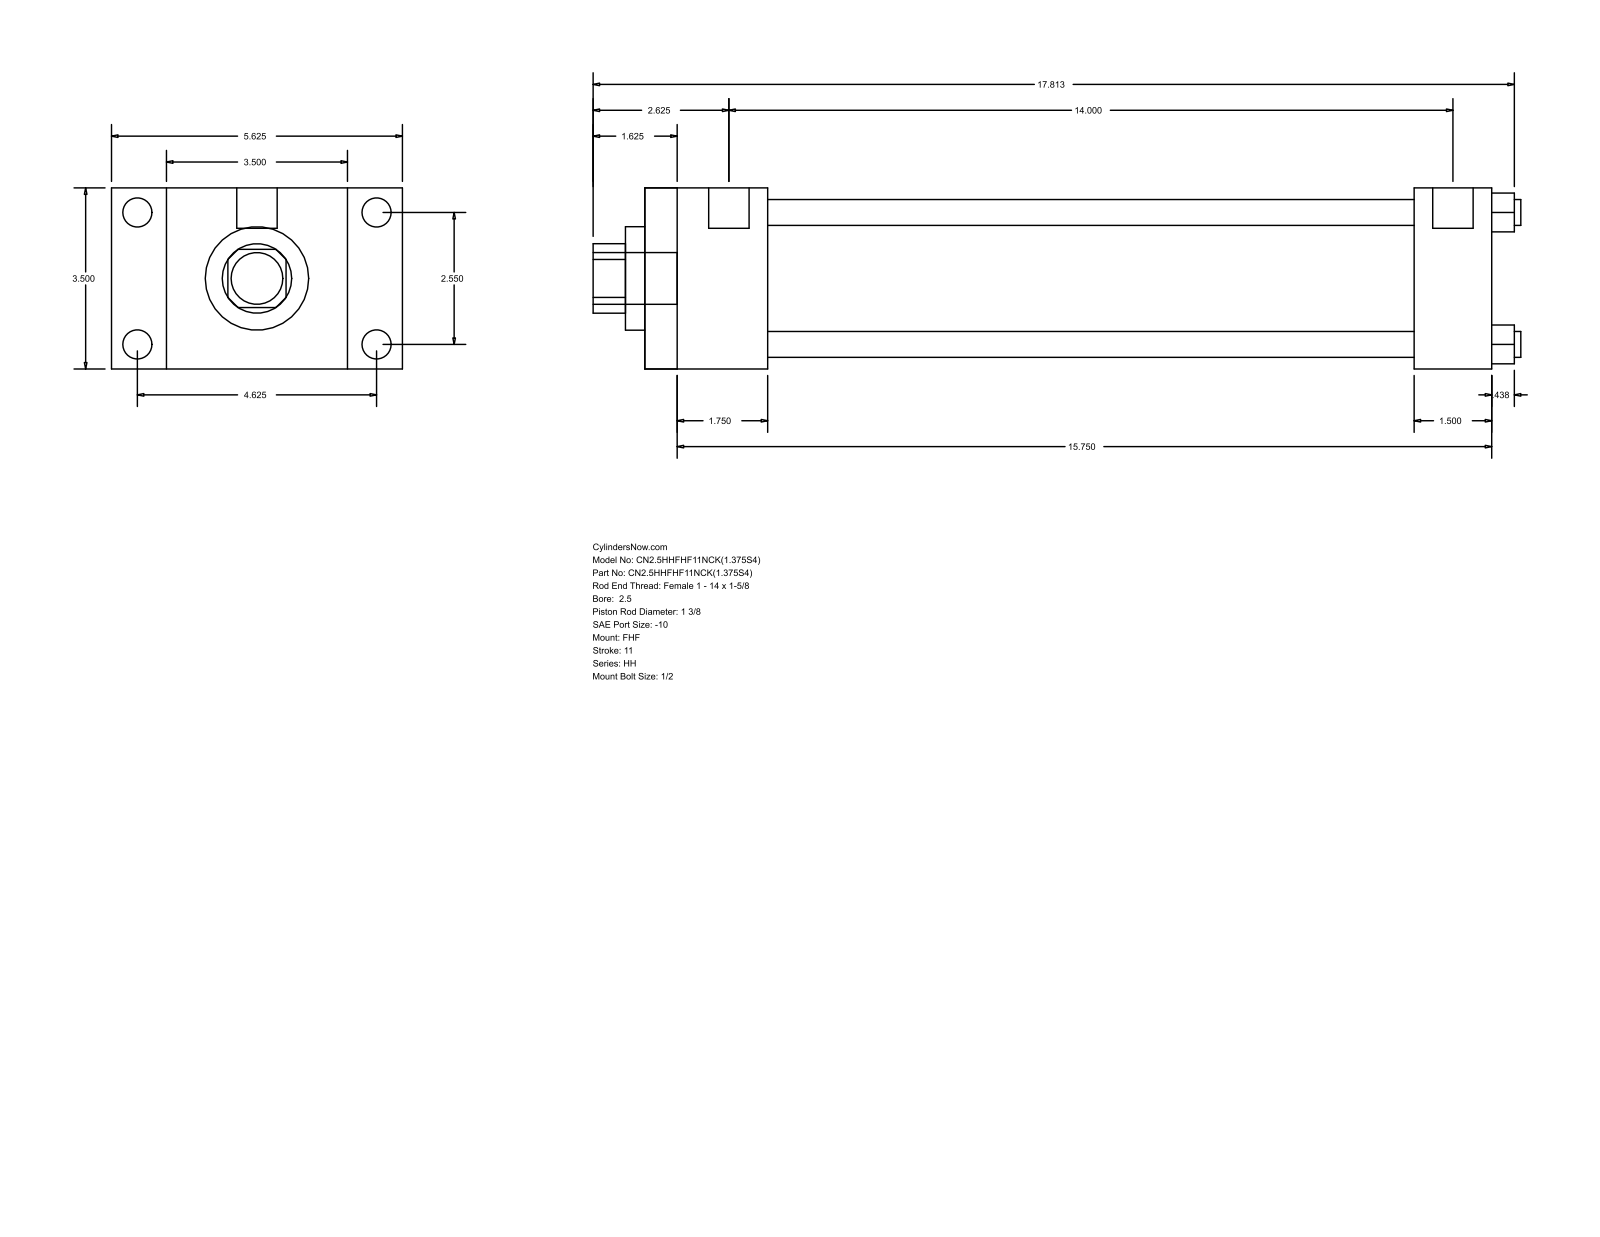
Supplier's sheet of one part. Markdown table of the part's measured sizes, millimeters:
| quantity | value |
| --- | --- |
| part name | HH_FHF__0250_1.375 |
| STEP written by | GSSL Pune (CONFIG_CONTROL_DESIGN) |
| units | millimeters |
| bodies | 0 solids, 88 faces (60 planar, 28 cylindrical, 0 other) |
| overall size | 455.61 × 142.88 × 88.9 |
| round holes (diameter × count) | 12.7 × 4, 34.92 × 1, 50.8 × 1, 73.03 × 1 |
| round bosses / shafts (diameter × count) | 14.3 × 4, 5.56 × 4, 19.84 × 2, 25.4 × 1 |
| partial cylindrical surfaces (radius × count) | 17.06 × 1 |
| main face-to-face distances | 88.9, 60.32, 26.99, 115.89, 415.92, 355.6, 142.88, 377.83, 317.51, 38.09 |
| hole center spacings | 45.79, 64.76, 91.58 |
